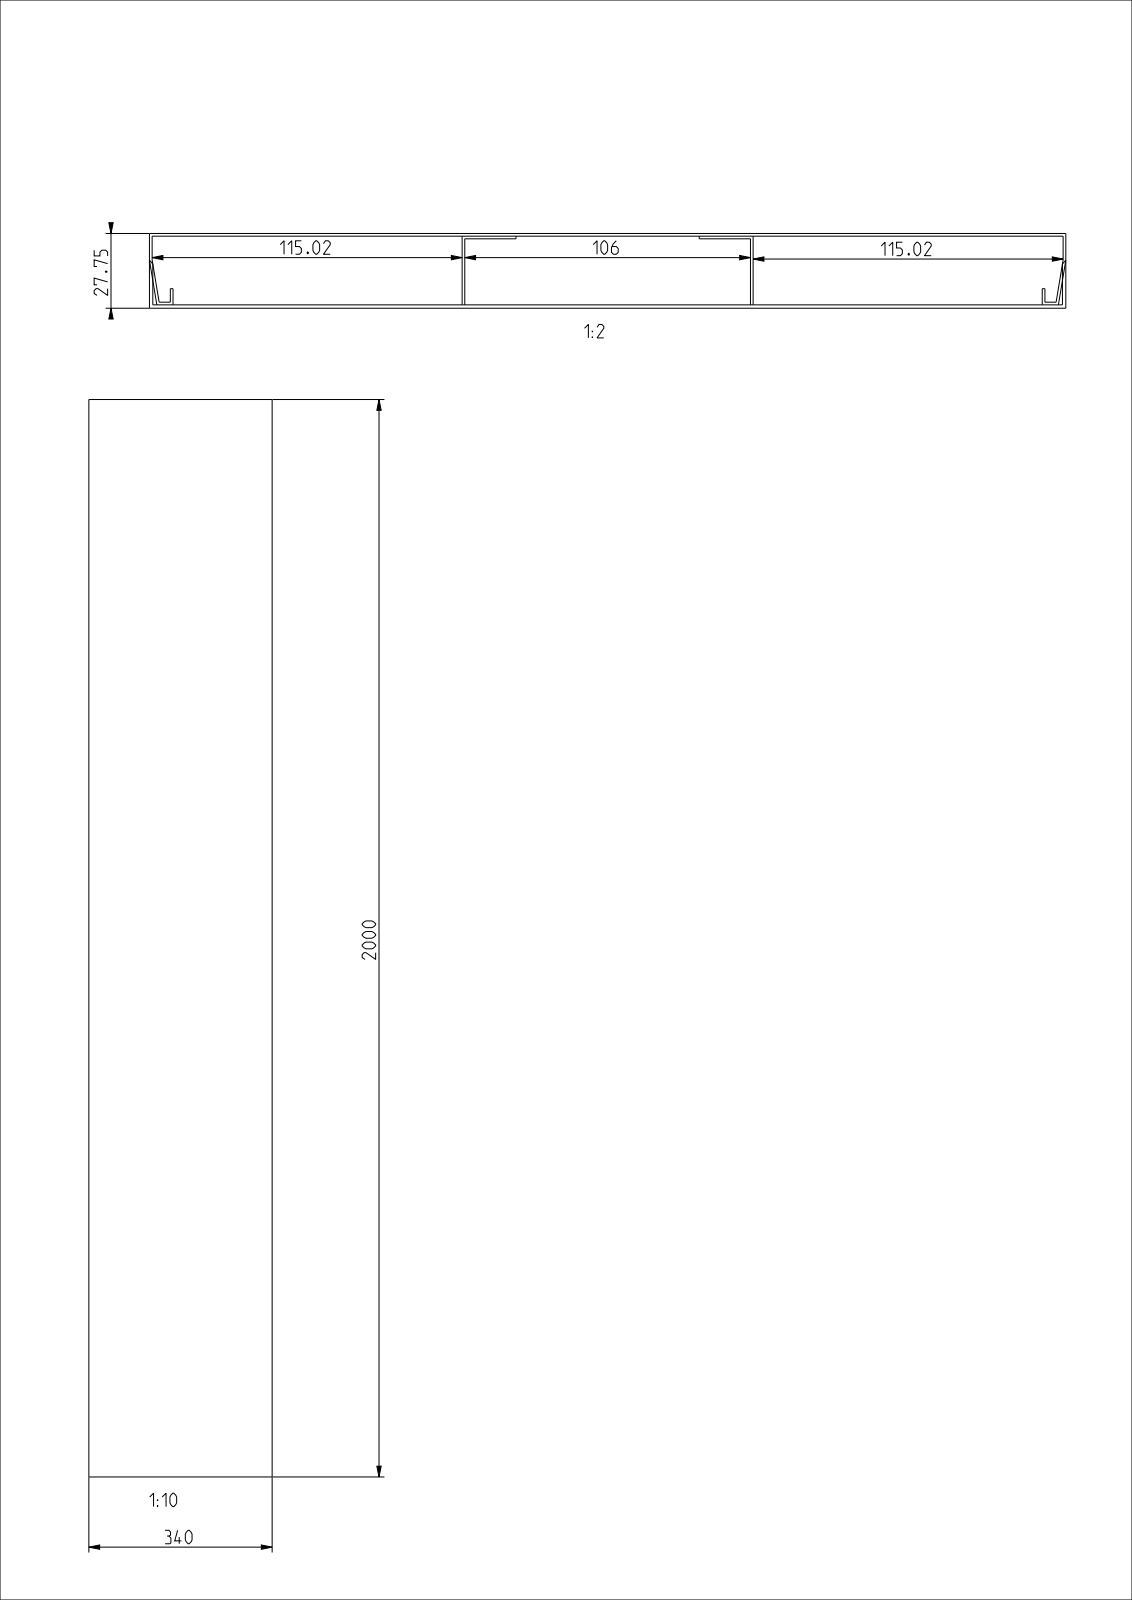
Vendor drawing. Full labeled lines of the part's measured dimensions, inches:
Part name (STEP PRODUCT): UK340283KUN_OBERTEIL; UK340283KUN_UNTERTEIL; UK340283KUN_ASM
STEP written by: CREO PARAMETRIC BY PTC INC, 2022024 (AUTOMOTIVE_DESIGN)
Units: inches
Bodies: 2 solids, 46 faces (46 planar, 0 cylindrical, 0 other)
Overall size (bounding box): 78.74 × 13.386 × 1.093
Volume: 117.6 in³ · Surface area: 5 194 in²
Main face-to-face distances: 0.049, 0.039, 1.043, 1.093, 1.004, 1.053, 0.039, 4.568, 8.818, 4.606
